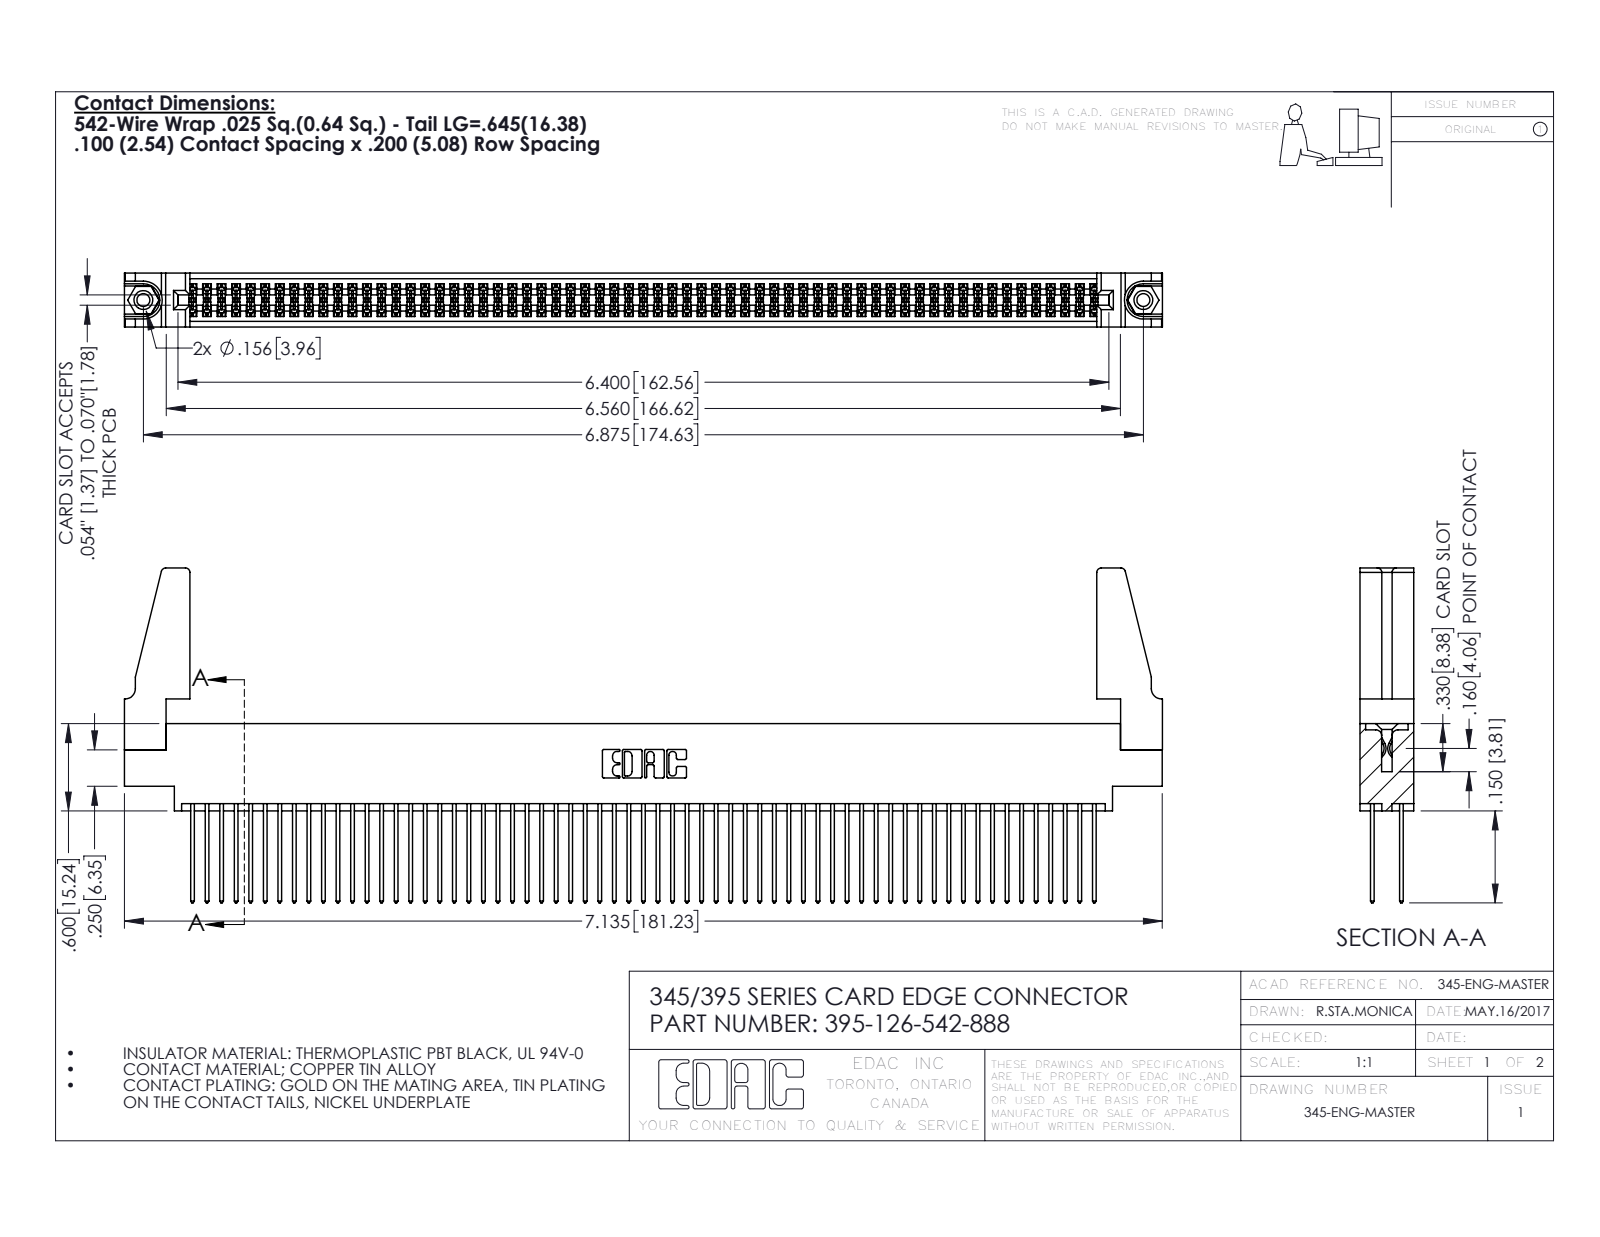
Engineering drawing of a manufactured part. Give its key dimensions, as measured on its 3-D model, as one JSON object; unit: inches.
{"part_name": "345 Part_0.170 Offset - 0.156 Dia-TH; 345-220-078_345-220-088; 395-126-542-888; 345-250-001_345-250-001-102 (+1 more)", "step_written_by": "SolidWorks 2016 (CONFIG_CONTROL_DESIGN)", "units": "inches", "bodies": {"solids": 131, "faces": 6554, "planar": 4314, "cylindrical": 2224, "other": 16}, "overall_size": [7.136, 2.302, 0.37], "volume_in3": 1.314, "surface_area_in2": 51.82, "round_holes": [[0.089, 2], [0.125, 2], [0.156, 2], [0.064, 1]], "round_bosses_or_shafts": [[0.155, 2]], "partial_cylinders_radius": [[0.006, 189], [0.01, 126], [0.01, 22], [0.03, 8], [0.007, 6], [0.031, 6], [0.026, 3], [0.014, 2]], "face_to_face_distances": [0.072, 0.298, 0.2, 0.098, 0.272, 0.025, 0.37, 0.225, 0.175, 0.149], "hole_center_spacings": [0.27, 6.639, 6.875]}
